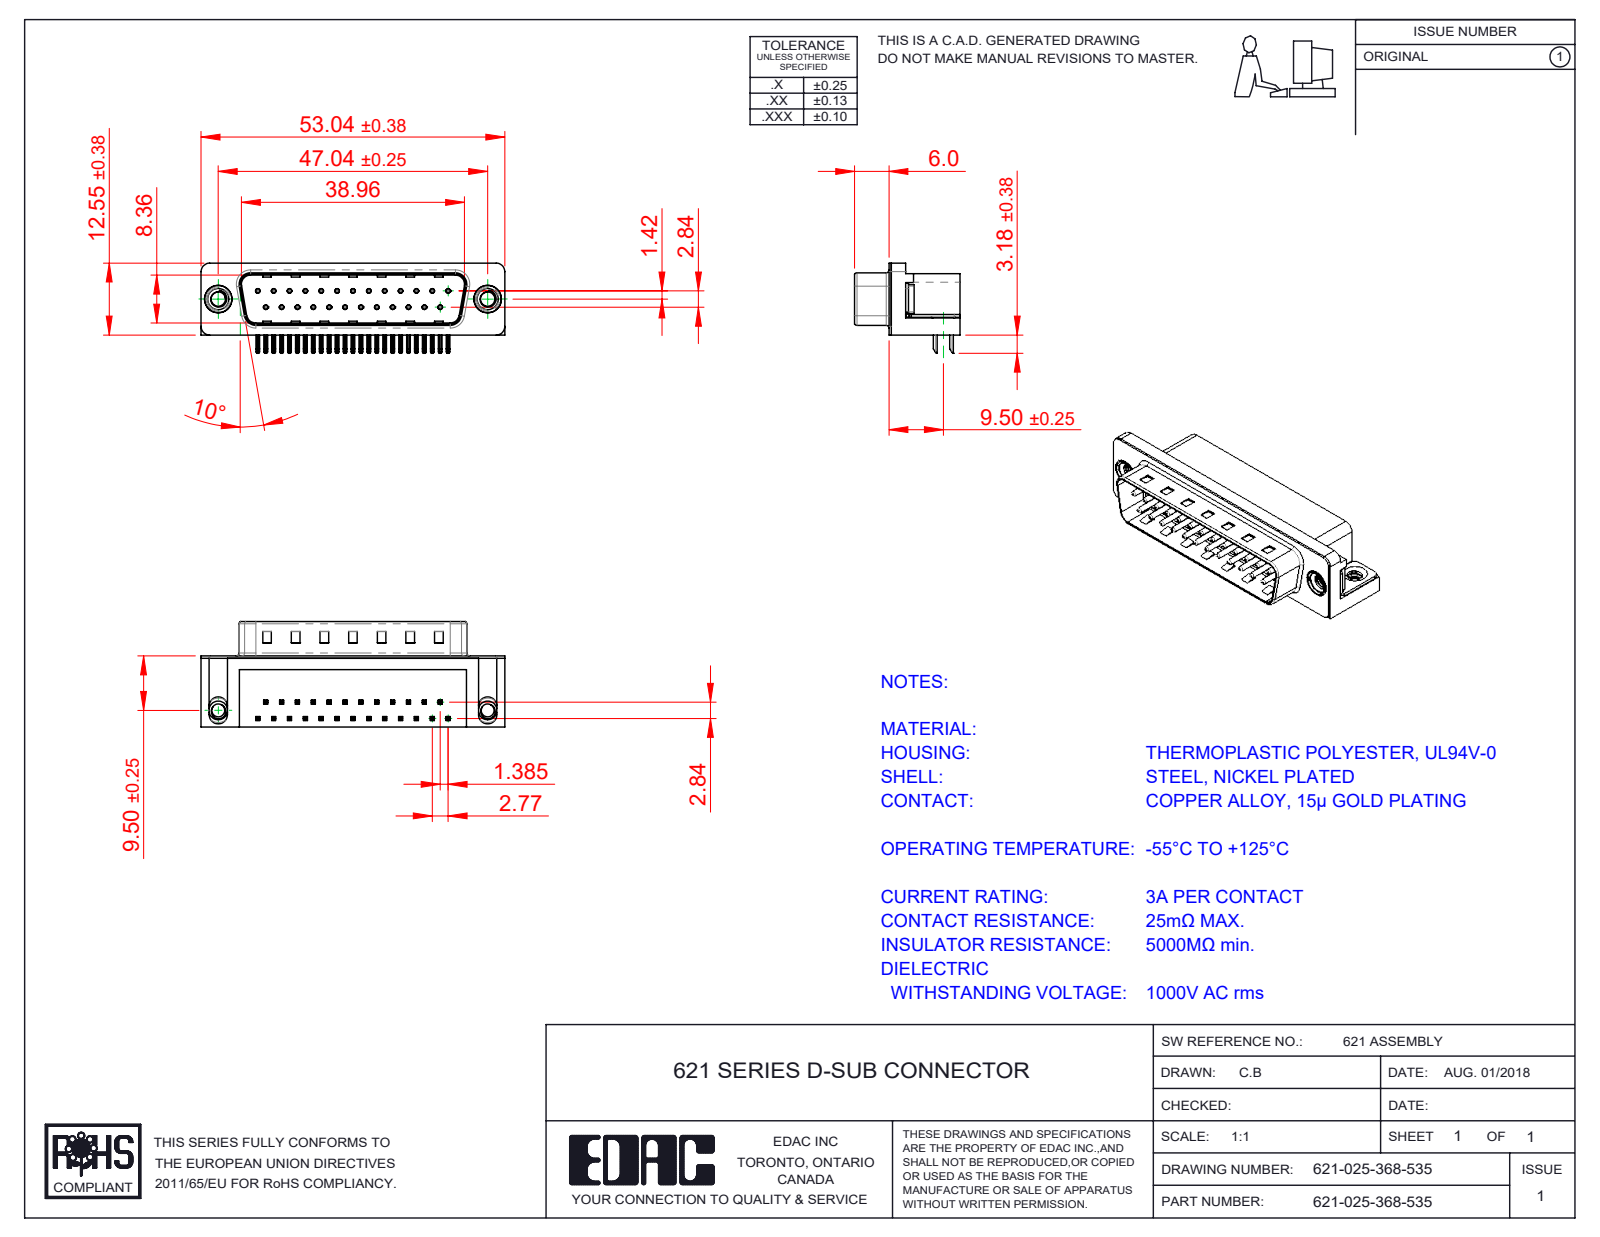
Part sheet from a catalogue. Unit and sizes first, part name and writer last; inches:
Units: inches
Overall size (bounding box): 2.088 × 0.724 × 0.64
Round holes (diameter × count): ⌀0.014 ×25, ⌀0.031 ×25, ⌀0.098 ×2, ⌀0.157 ×2, ⌀0.189 ×2, ⌀0.197 ×2
Round bosses / shafts (diameter × count): ⌀0.03 ×25, ⌀0.193 ×2, ⌀0.187 ×2, ⌀0.154 ×2
Partial cylindrical surfaces — rounded edges, fillets, slot ends (radius × count): R0.01 ×108, R0.005 ×50, R0.039 ×16, R0.02 ×14, R0.063 ×8, R0.059 ×7, R0.013 ×4, R0.035 ×4
Main face-to-face distances: 0.016, 0.472, 0.407, 0.083, 0.345, 0.412, 0.428, 0.067, 0.488, 0.354
Hole centre spacings: 0.124, 0.109, 0.218, 0.327, 0.436, 0.545, 0.654, 0.198
Volume: 0.387 in³ · Surface area: 11.92 in²
Bodies: 31 solids, 2303 faces (1437 planar, 671 cylindrical, 195 other)
Part name (STEP PRODUCT): 621-025-368-535; 621 Contact Bottom; 621 Contact Top; 621 Housing_25 Socket (+3 more)
STEP written by: SolidWorks 2016 (CONFIG_CONTROL_DESIGN)
